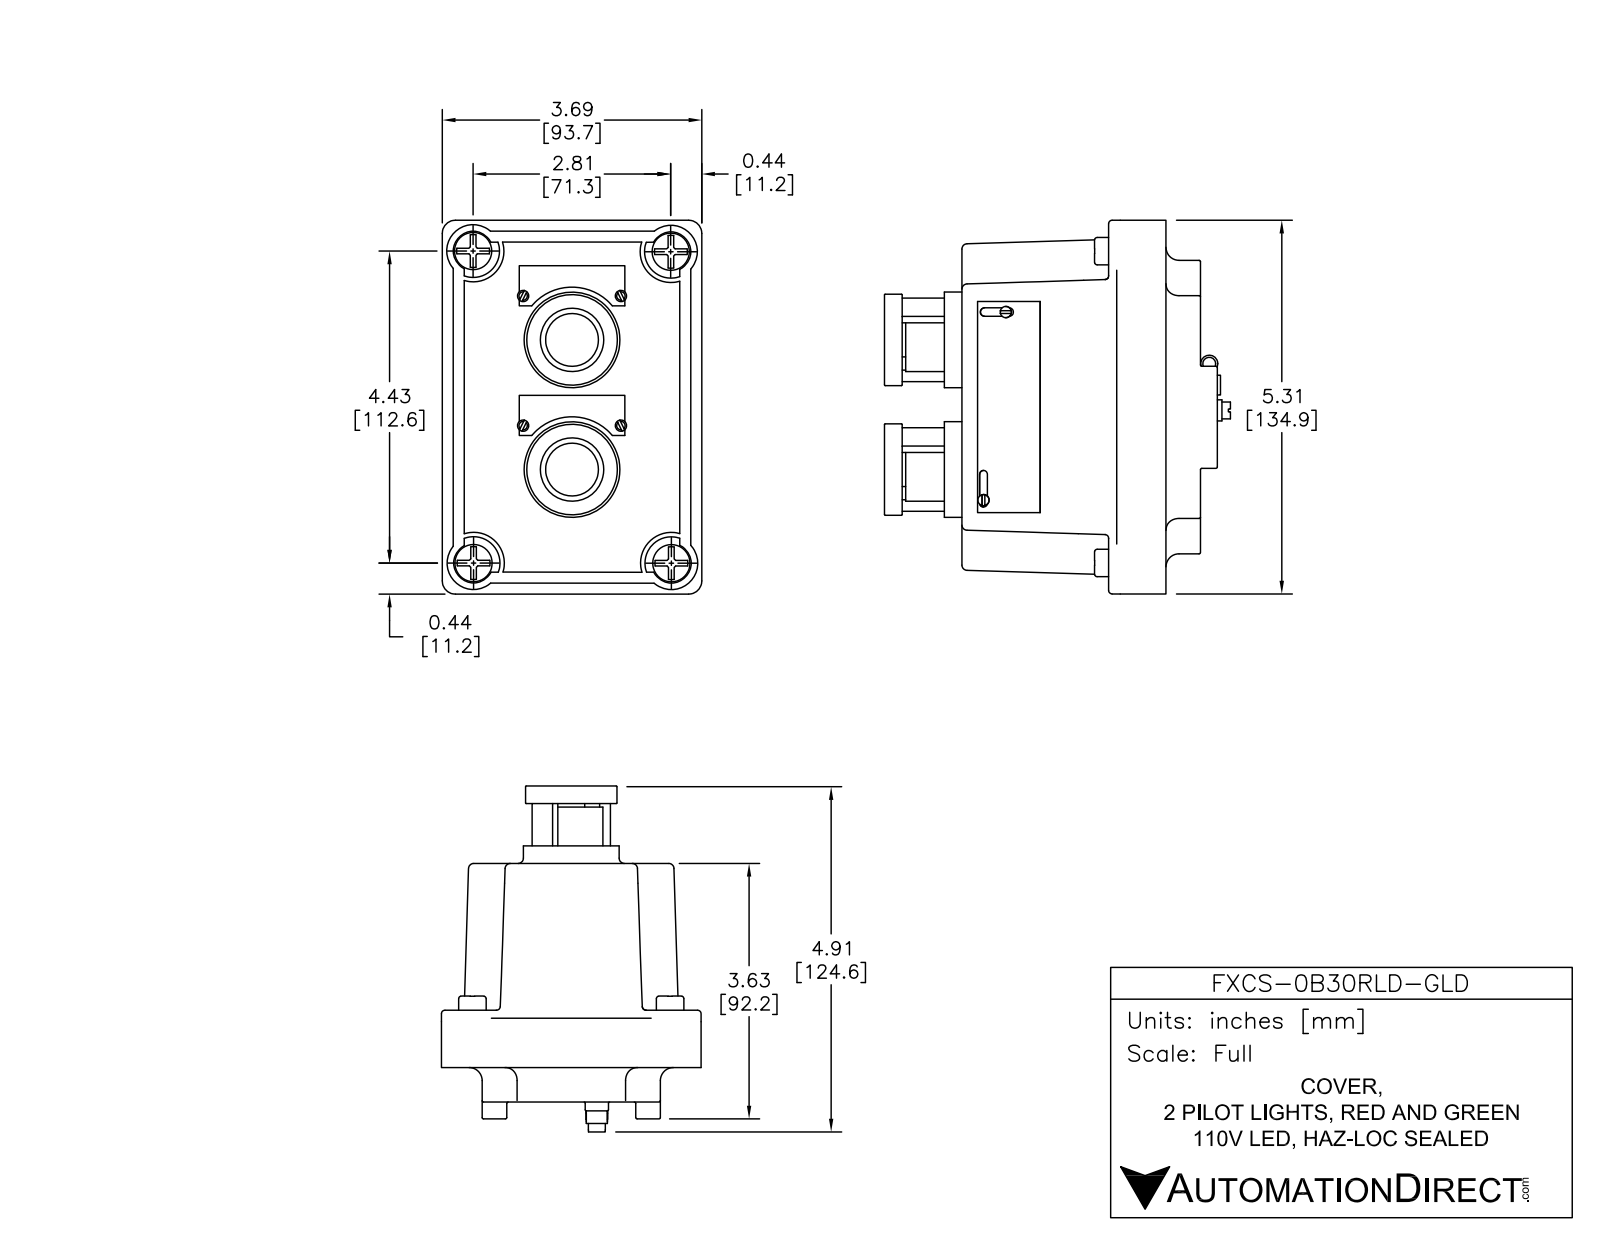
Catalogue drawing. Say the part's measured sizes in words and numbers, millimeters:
The part is named "FXCS-0B30RLD-GLD". Its 3-D file was written by "SolidWorks 2015 (AUTOMOTIVE_DESIGN)". It is 1 solid with 746 faces: 314 planar, 165 cylindrical and 267 other. Overall it measures 134.9 by 126.7 by 93.7 millimeters. Its volume is 817 100 cubic millimeters and its surface area 68 650 square millimeters. Round holes: 8 of diameter 4.1, 1 of diameter 5, 1 of diameter 22.9, 1 of diameter 23.9. Round bosses or shafts: 8 of diameter 4.1, 4 of diameter 9.9, 2 of diameter 34.5, 2 of diameter 33, 1 of diameter 22.9, 1 of diameter 8.4, 1 of diameter 7.6, 1 of diameter 6.1. Partial cylindrical surfaces (rounded edges, fillets, slot ends): 22 of radius 0.5, 12 of radius 1.3, 4 of radius 1.4, 4 of radius 1.5, 4 of radius 1.9, 4 of radius 4.7, 4 of radius 10.7, 3 of radius 16.6. The main face-to-face distances are 12.4, 86.1, 73.7, 0.5, 93.7, 14.7, 79, 6.4, 30.2, 17.8. The hole center spacings are 6.4, 55.8, 12.7, 55.4, 56.9, 19.1, 29.7, 32.5.
